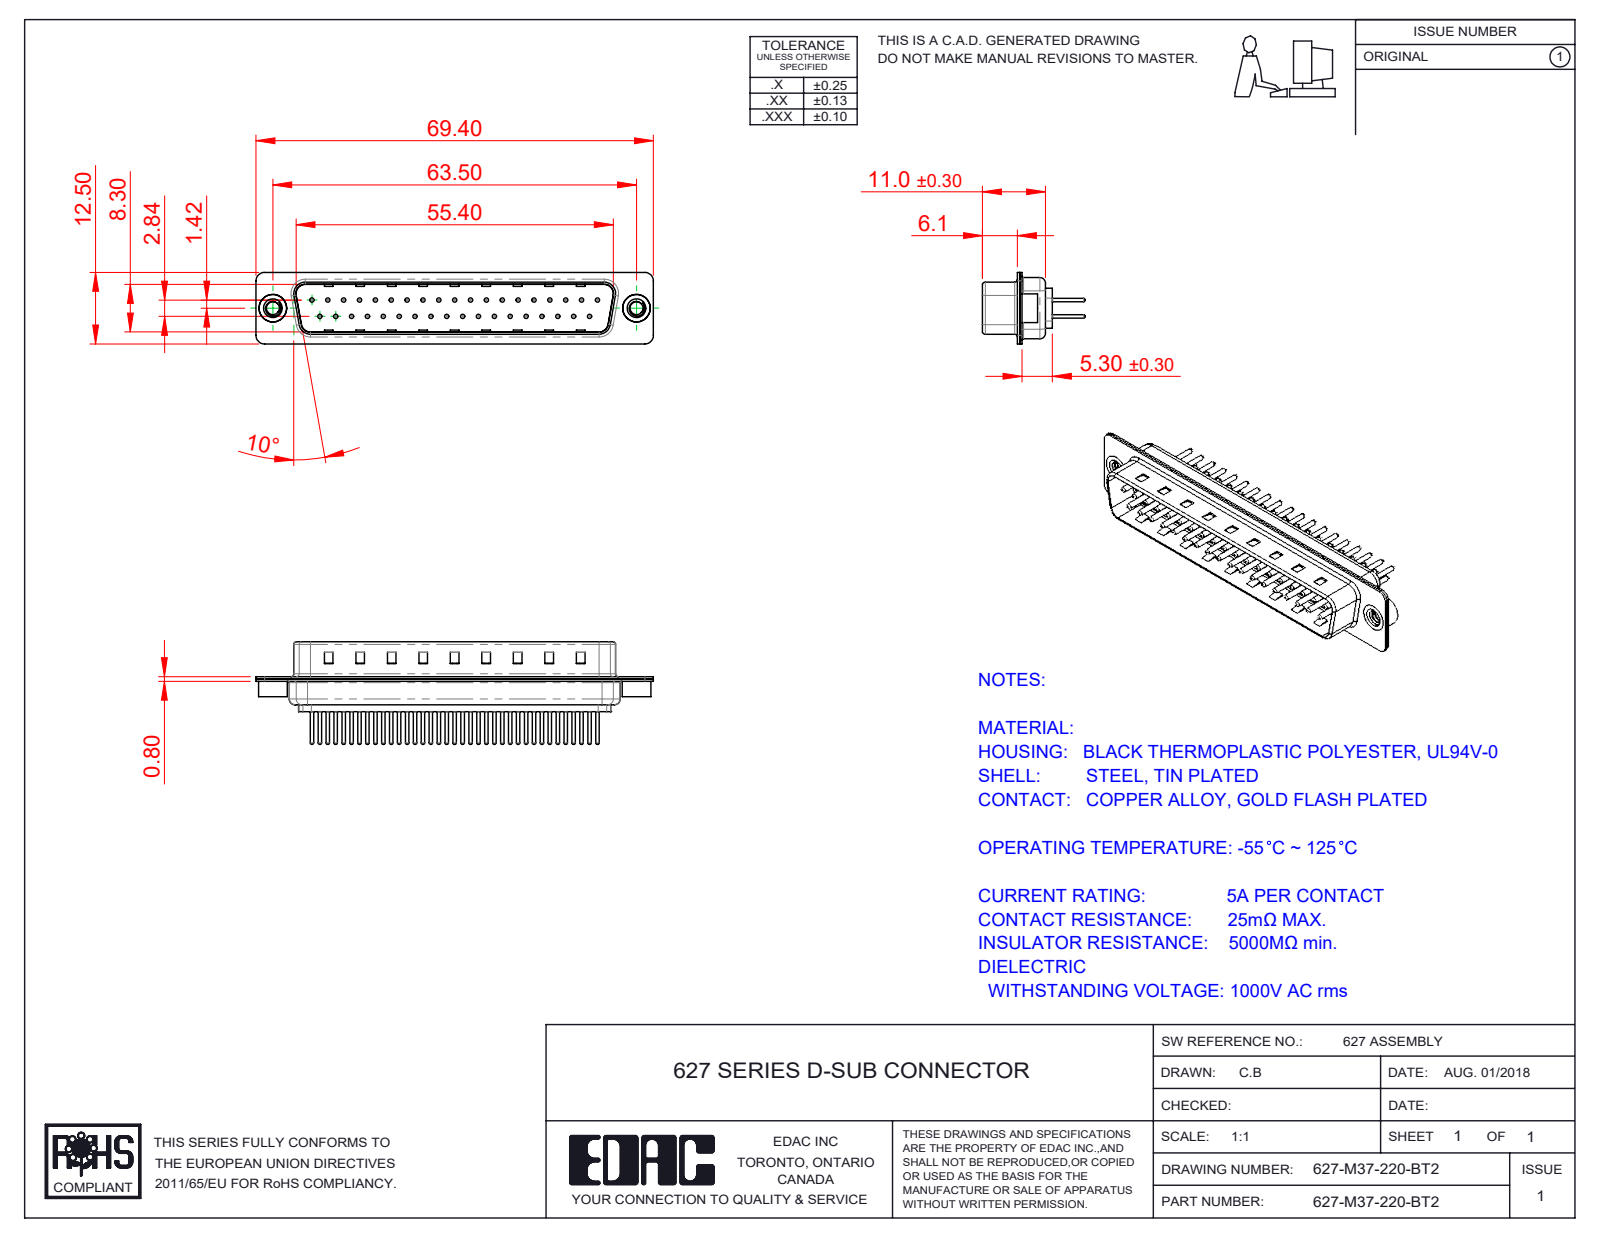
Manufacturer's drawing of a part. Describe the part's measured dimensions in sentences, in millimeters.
The part is named "627-M37-220-BT2; 627M Shell Rear_37 Contacts; 627M Contact Row 2_20; 627M Contact Row 1_20 (+3 more)". Its 3-D file was written by "SolidWorks 2020 (CONFIG_CONTROL_DESIGN)". It is 42 solids with 1781 faces: 462 planar, 659 cylindrical and 660 other. Overall it measures 69.4 by 17.9 by 12.5 millimeters. Its volume is 3 768 cubic millimeters and its surface area 9 269 square millimeters. Round holes: 37 of diameter 0.75, 37 of diameter 1.6, 37 of diameter 2, 2 of diameter 2.26, 2 of diameter 4, 2 of diameter 4.8. Round bosses or shafts: 37 of diameter 1.5, 37 of diameter 0.6, 2 of diameter 5, 2 of diameter 4.9. Partial cylindrical surfaces (rounded edges, fillets, slot ends): 16 of radius 1.5, 12 of radius 2, 8 of radius 0.5, 8 of radius 1.6, 4 of radius 0.25, 4 of radius 0.6, 4 of radius 0.65, 4 of radius 0.9. The main face-to-face distances are 0.4, 0.8, 9.5, 9.1, 8.7, 9.9, 1.2, 5.7, 0.75, 0.35. The hole center spacings are 2.77, 5.54, 3.16, 8.31, 11.08, 13.85, 16.62, 19.39.
